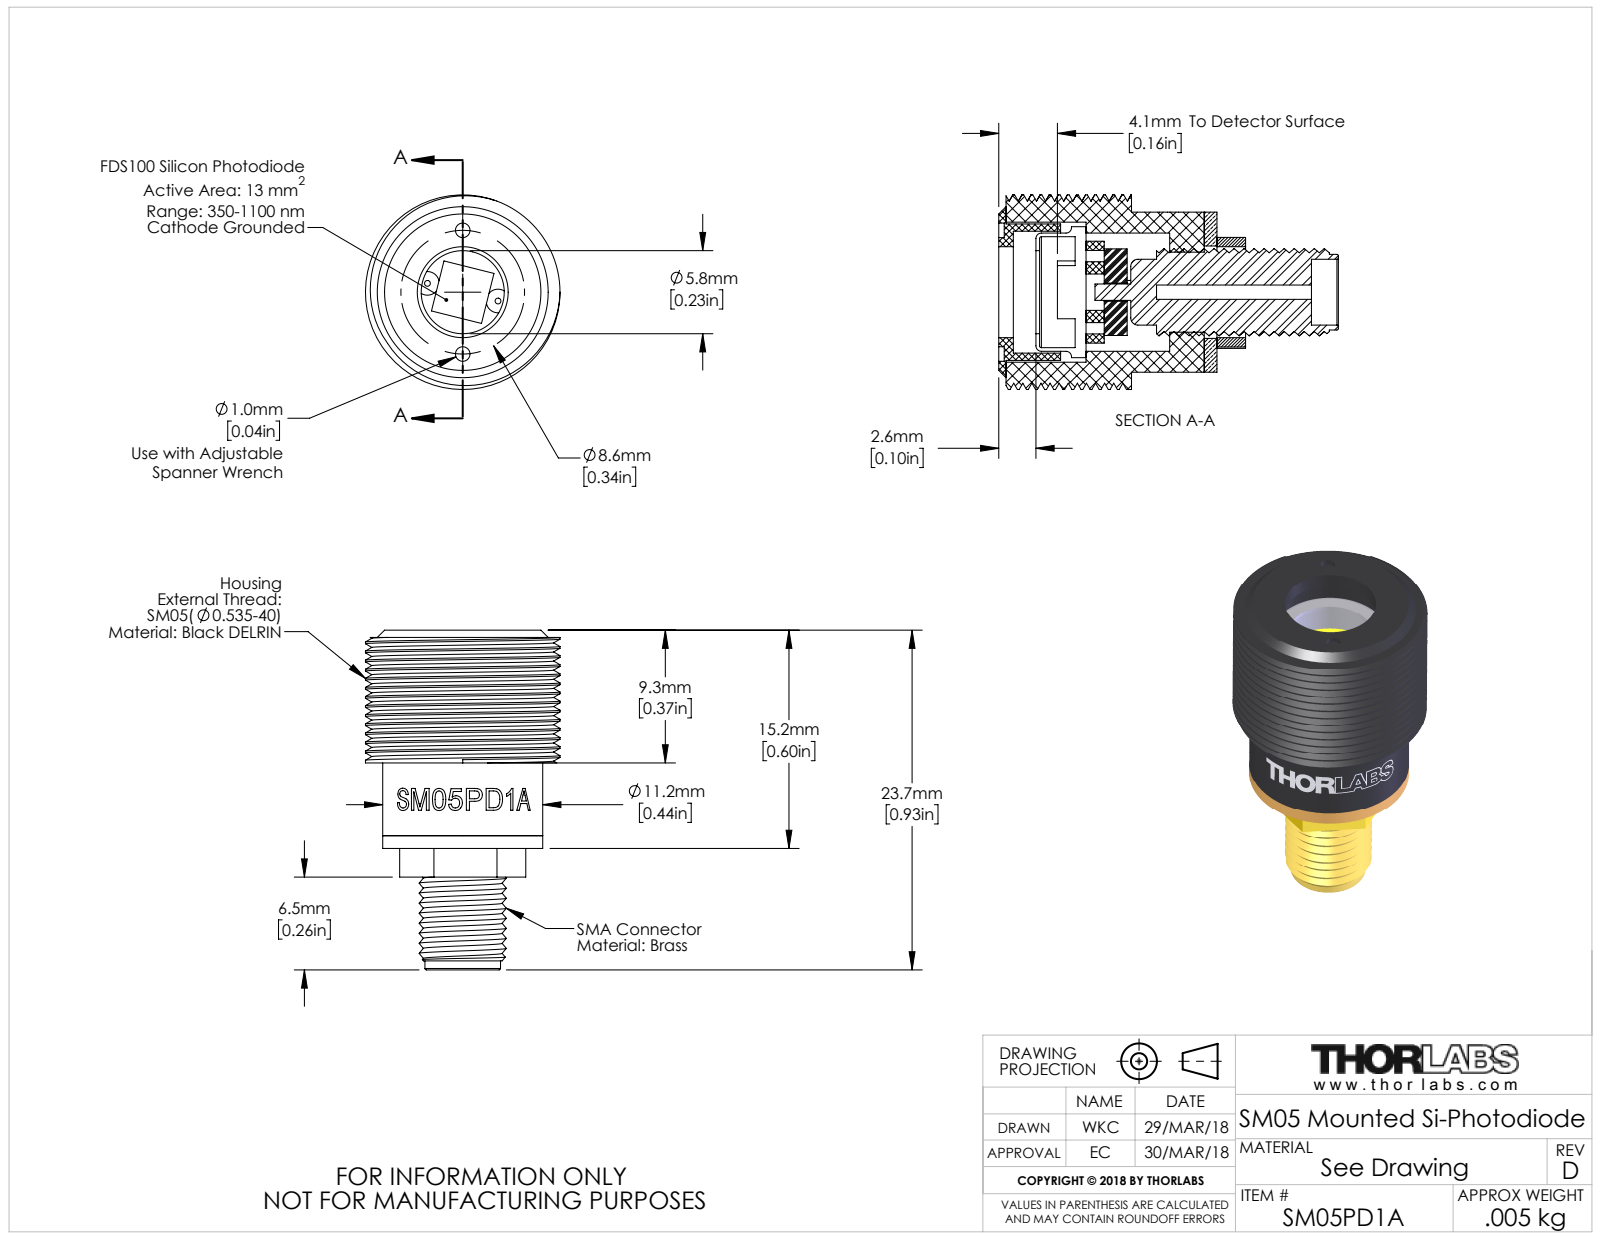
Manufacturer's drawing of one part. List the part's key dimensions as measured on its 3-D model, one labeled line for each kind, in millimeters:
Part name (STEP PRODUCT): 8770-E0W
STEP written by: SolidWorks 2016 (AUTOMOTIVE_DESIGN)
Units: millimetres
Bodies: 6 solids, 125 faces (51 planar, 58 cylindrical, 16 other)
Overall size (bounding box): 23.5 × 13.6 × 13.6
Volume: 1 500 mm³ · Surface area: 2 843 mm²
Round holes (diameter × count): ⌀1 ×2, ⌀1.7 ×2, ⌀1 ×1, ⌀4.6 ×1, ⌀5.6 ×1, ⌀5.8 ×1, ⌀6.4 ×1, ⌀6.5 ×1, ⌀7.7 ×1, ⌀8.3 ×1, ⌀8.5 ×1, ⌀9.8 ×1
Round bosses / shafts (diameter × count): ⌀0.4 ×3, ⌀13.6 ×1, ⌀11.2 ×1, ⌀9.5 ×1, ⌀9.1 ×1, ⌀8.3 ×1, ⌀5.3 ×1, ⌀1.1 ×1
Partial cylindrical surfaces — rounded edges, fillets, slot ends (radius × count): R0.1 ×4
Main face-to-face distances: 8.5, 0.5, 0.9, 9.4, 14.7, 13.8, 5.3, 15.2, 14.4, 5.8
Hole centre spacings: 2.5, 3.1, 4.3, 6.4, 5.1, 8.6
